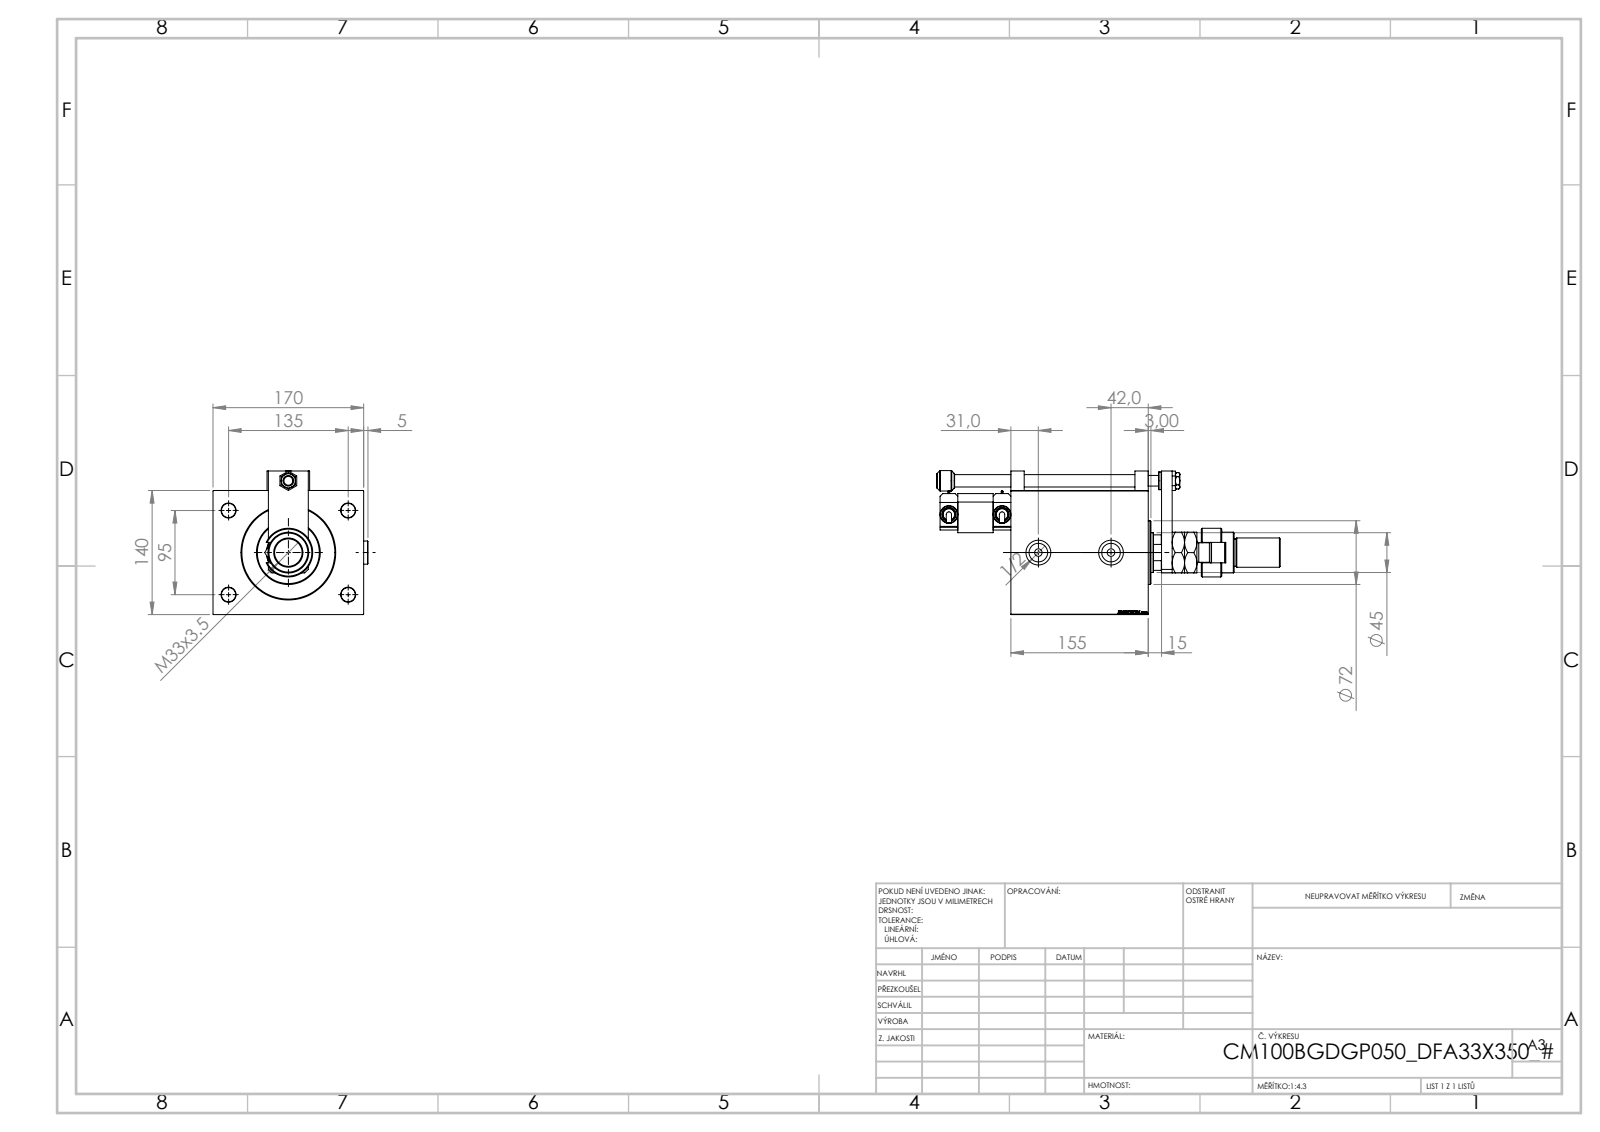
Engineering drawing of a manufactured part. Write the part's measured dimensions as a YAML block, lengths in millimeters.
part_name: "V450CM_B_Body; Zatka_OIL_PORT; MFA; P_V_Z_DFA (+7 more)"
step_written_by: "SolidWorks 2019 (CONFIG_CONTROL_DESIGN)"
units: millimeters
bodies: {solids: 18, faces: 1248, planar: 576, cylindrical: 143, other: 529}
overall_size: [387.6, 174.9, 162.5]
volume: 3720000
surface_area: 372606
round_holes:
  - {diameter: 4, count: 4}
  - {diameter: 8, count: 4}
  - {diameter: 16, count: 4}
  - {diameter: 8.5, count: 2}
  - {diameter: 20.96, count: 2}
  - {diameter: 28, count: 2}
  - {diameter: 12, count: 1}
  - {diameter: 13, count: 1}
  - {diameter: 14, count: 1}
  - {diameter: 31.5, count: 1}
  - {diameter: 33, count: 1}
  - {diameter: 39, count: 1}
round_bosses_or_shafts:
  - {diameter: 20, count: 3}
  - {diameter: 26, count: 2}
  - {diameter: 16, count: 2}
  - {diameter: 14, count: 2}
  - {diameter: 6, count: 2}
  - {diameter: 72, count: 1}
  - {diameter: 55, count: 1}
  - {diameter: 46, count: 1}
partial_cylinders:
  - {radius: 3, count: 1}
  - {radius: 11.5, count: 1}
  - {radius: 22, count: 1}
face_to_face_distances: [140, 170, 155, 26, 129, 15, 65, 60, 114, 92]
hole_center_spacings: [82.54, 20, 75.36, 95, 135, 140, 141.42, 145.15]
